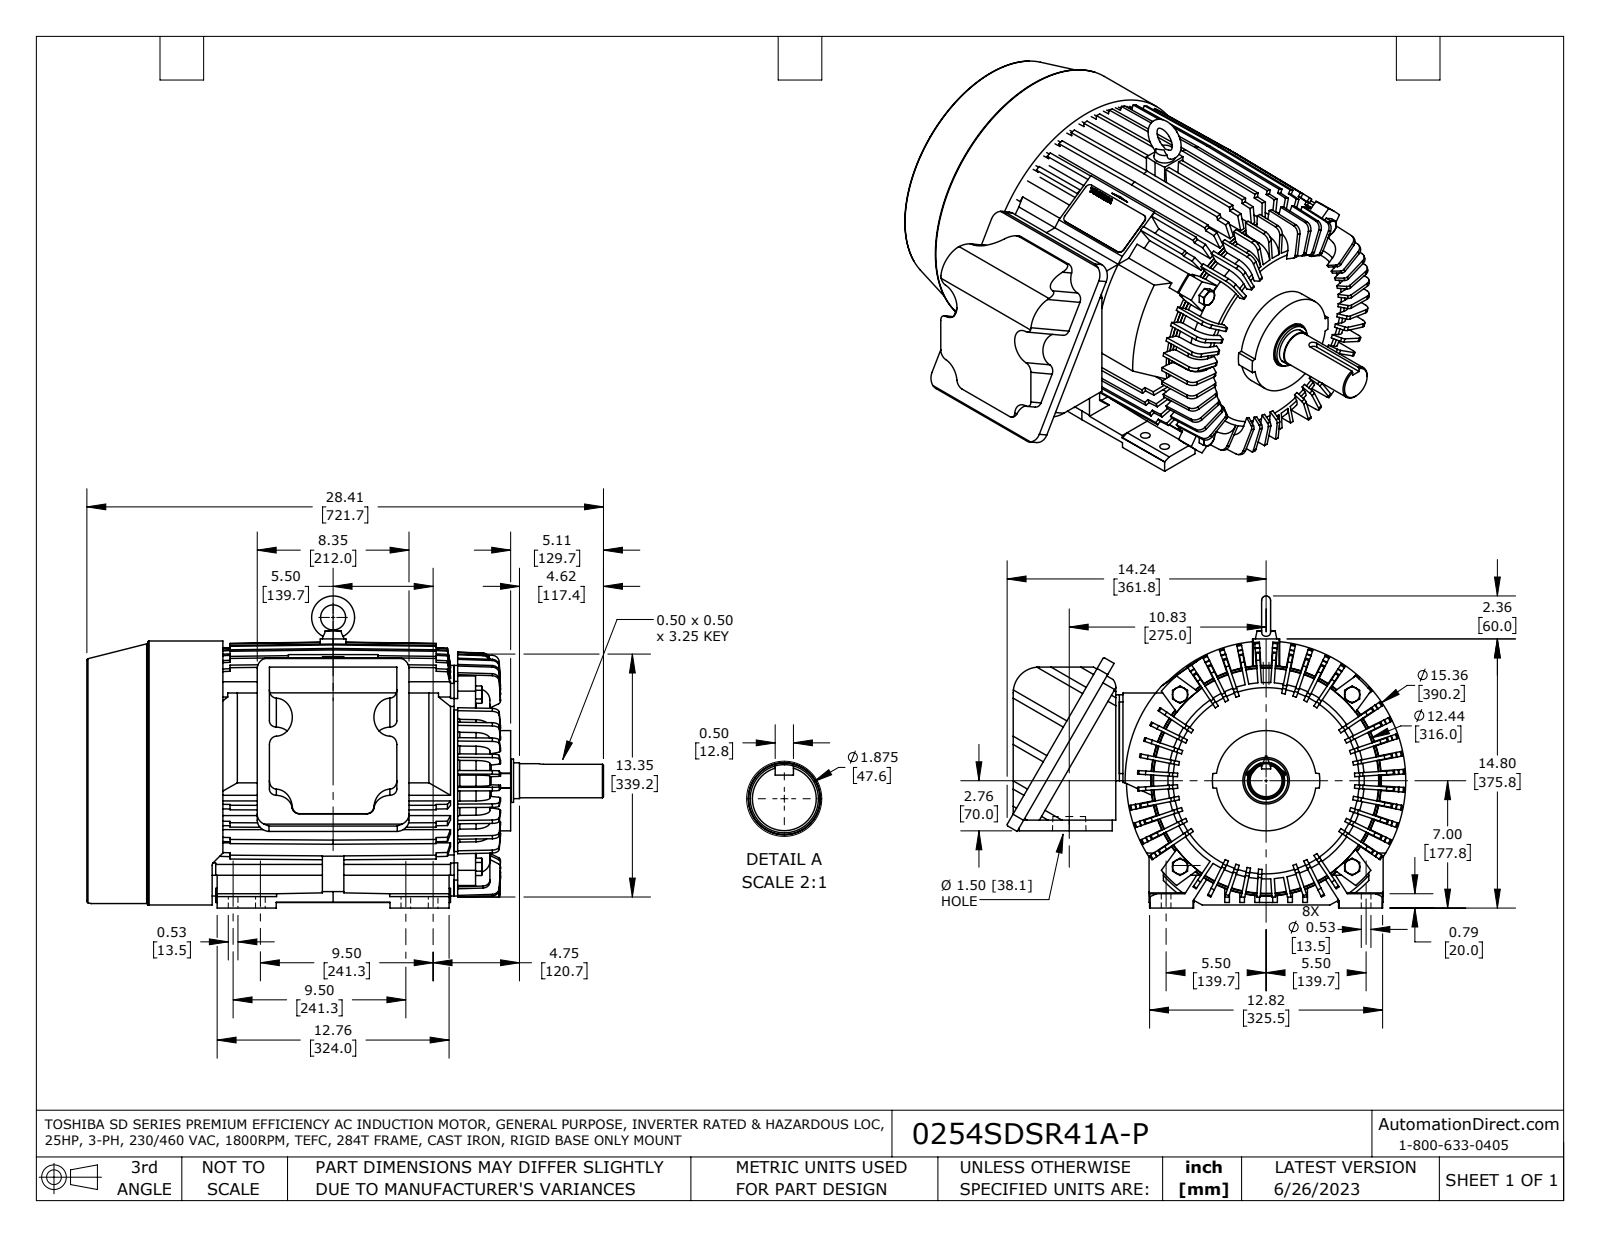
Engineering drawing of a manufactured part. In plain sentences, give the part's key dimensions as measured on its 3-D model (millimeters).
The part is named "MDSLV001-05-46P-F1-Bottom nc bod broke rep1". Its 3-D file was written by "SolidWorks 2021 (AUTOMOTIVE_DESIGN)". It is 13 solids with 3154 faces: 2342 planar, 250 cylindrical and 562 other. Overall it measures 721.7 by 556.9 by 435.8 millimeters. Its volume is 66 320 000 cubic millimeters and its surface area 2 594 000 square millimeters. Round holes: 8 of diameter 9, 8 of diameter 13.5, 4 of diameter 2.2, 4 of diameter 10.1, 4 of diameter 14, 1 of diameter 12, 1 of diameter 13.8, 1 of diameter 21, 1 of diameter 50.5, 1 of diameter 65, 1 of diameter 67.6, 1 of diameter 100. Round bosses or shafts: 1 of diameter 390.2, 1 of diameter 322, 1 of diameter 311, 1 of diameter 140, 1 of diameter 70, 1 of diameter 60.5, 1 of diameter 60, 1 of diameter 50. Partial cylindrical surfaces (rounded edges, fillets, slot ends): 26 of radius 10, 6 of radius 0.5, 6 of radius 1.1, 6 of radius 1.4, 6 of radius 23, 4 of radius 0.5, 4 of radius 2.3, 4 of radius 6.4. The main face-to-face distances are 15, 338, 323, 6.5, 331, 316, 7, 6.5, 175, 5. The hole center spacings are 231.7, 279.4, 12.5, 38.1, 60, 84.9, 157.5, 170.
